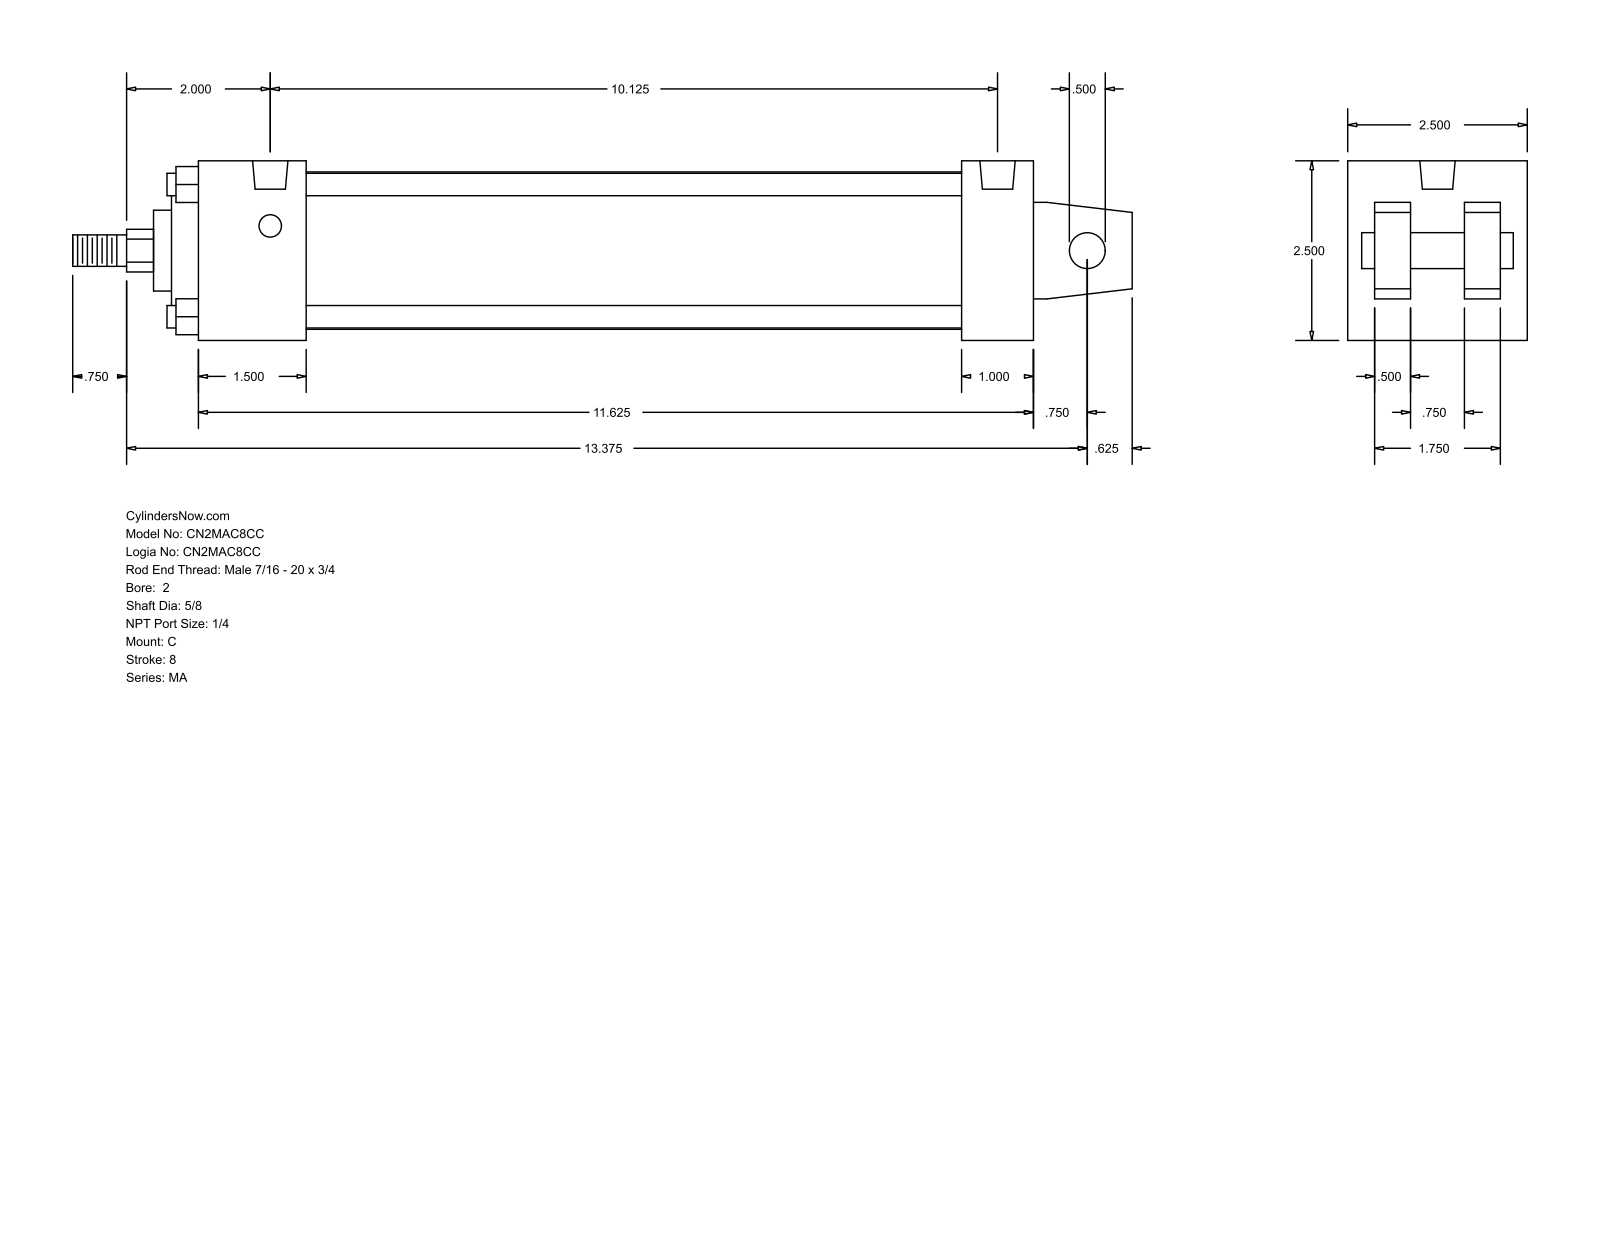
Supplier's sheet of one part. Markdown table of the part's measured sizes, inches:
| quantity | value |
| --- | --- |
| part name | MA_C__0200_0.625 |
| STEP written by | GSSL Pune (CONFIG_CONTROL_DESIGN) |
| units | inches |
| bodies | 0 solids, 105 faces (77 planar, 28 cylindrical, 0 other) |
| overall size | 14.75 × 2.5 × 2.5 |
| round holes (diameter × count) | 0.313 × 4, 0.492 × 2 |
| round bosses / shafts (diameter × count) | 0.313 × 4, 2.19 × 1, 2 × 1, 1.125 × 1, 0.625 × 1, 0.5 × 1, 0.437 × 1 |
| partial cylindrical surfaces (radius × count) | 0.297 × 1 |
| main face-to-face distances | 2.5, 0.375, 0.5, 0.875, 1.625, 2.125, 1.25, 1.5, 11.625, 10.125 |
| hole center spacings | 10.125 |
